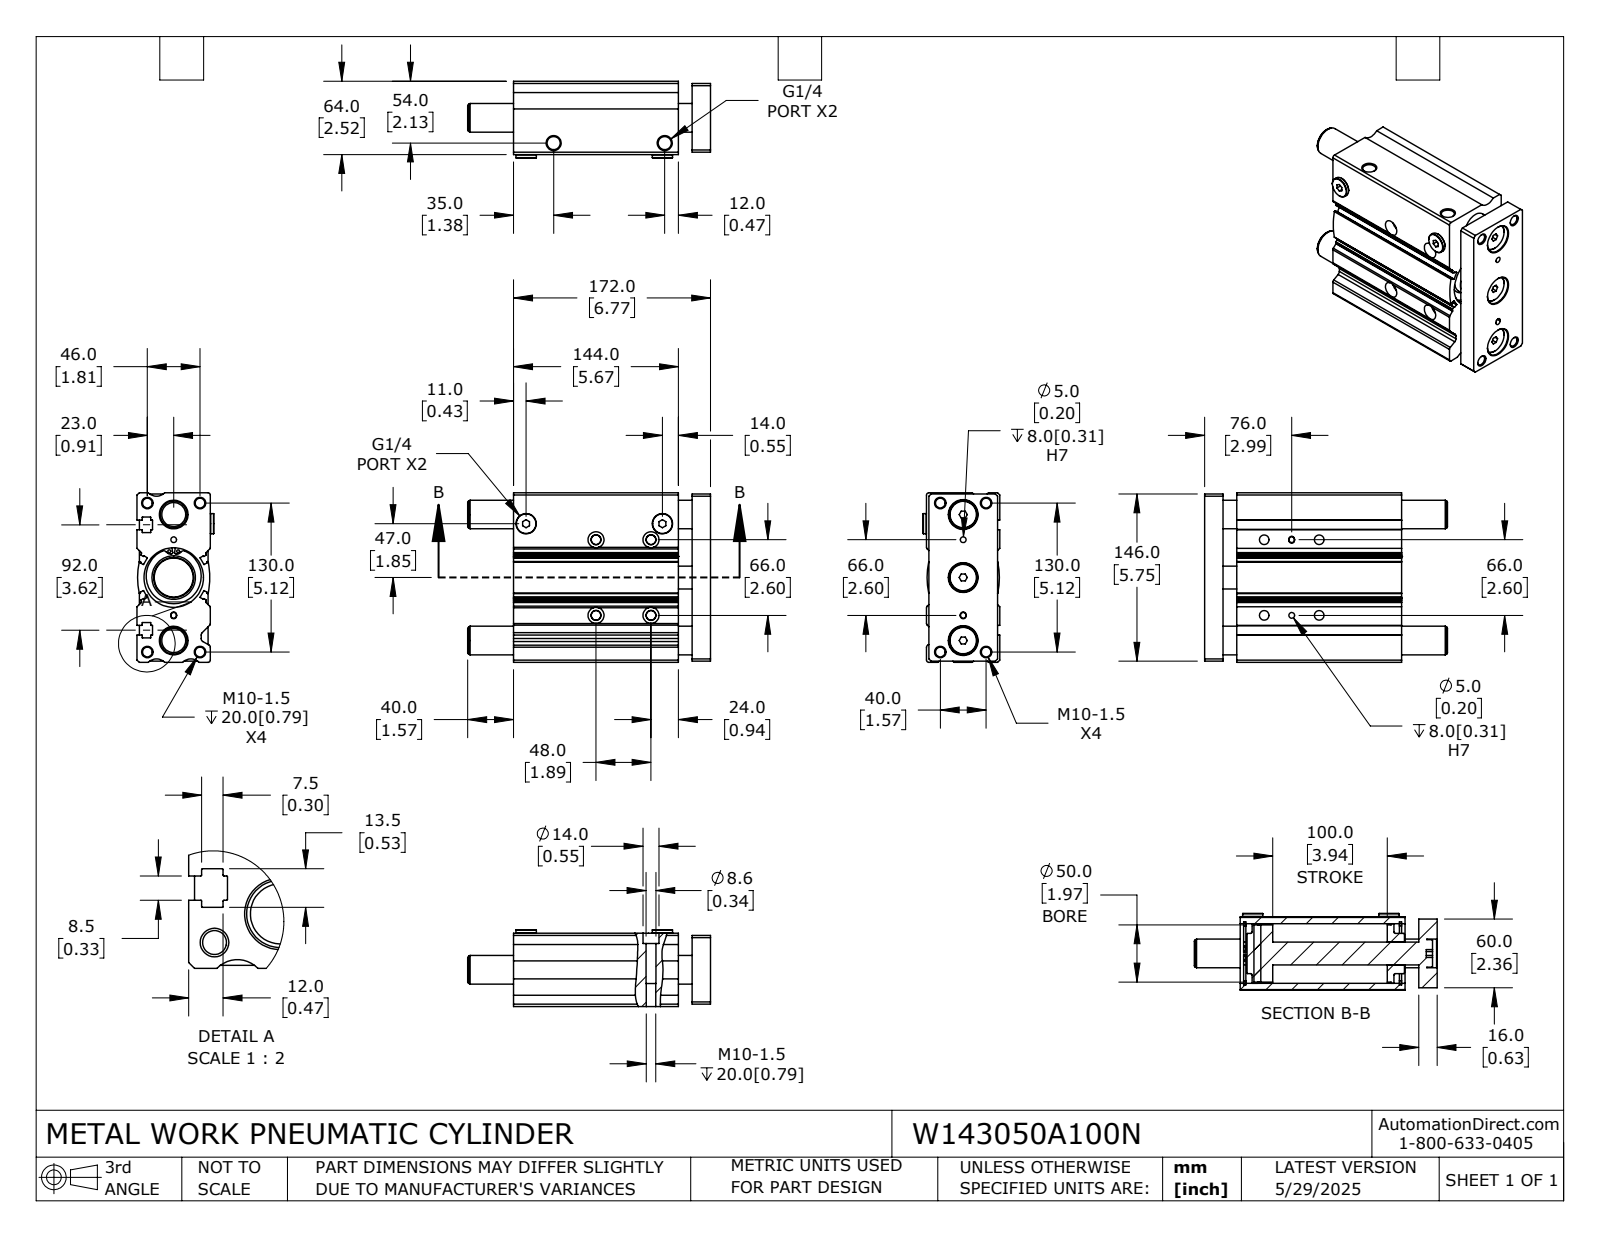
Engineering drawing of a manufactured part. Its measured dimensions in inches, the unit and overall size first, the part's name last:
Units: inches
Overall size (bounding box): 8.346 × 5.827 × 2.638
Round holes (diameter × count): ⌀0.33 ×12, ⌀0.098 ×4, ⌀0.197 ×4, ⌀0.339 ×4, ⌀0.551 ×4, ⌀0.984 ×3, ⌀0.451 ×2, ⌀1.89 ×2, ⌀0.787 ×1
Round bosses / shafts (diameter × count): ⌀0.945 ×3, ⌀0.697 ×2, ⌀2.165 ×1, ⌀2.047 ×1, ⌀1.969 ×1, ⌀1.378 ×1
Partial cylindrical surfaces — rounded edges, fillets, slot ends (radius × count): R0.012 ×44, R0.02 ×12, R0.118 ×10, R0.079 ×6, R2.677 ×6, R0.039 ×4, R0.098 ×4, R0.394 ×3
Main face-to-face distances: 0.472, 2.52, 5.669, 0.63, 6.142, 0.079, 1.102, 6.772, 0.098, 0.236
Hole centre spacings: 0.118, 0.424, 0.869, 0.88, 0.916, 0.945, 0.963, 0.987
Volume: 73.72 in³ · Surface area: 369.6 in²
Bodies: 6 solids, 466 faces (186 planar, 224 cylindrical, 56 other)
Part name (STEP PRODUCT): W143050A100N_BODY; W143050A100N_ROD; W143050A100N
STEP written by: SolidWorks 2024 (CONFIG_CONTROL_DESIGN)
